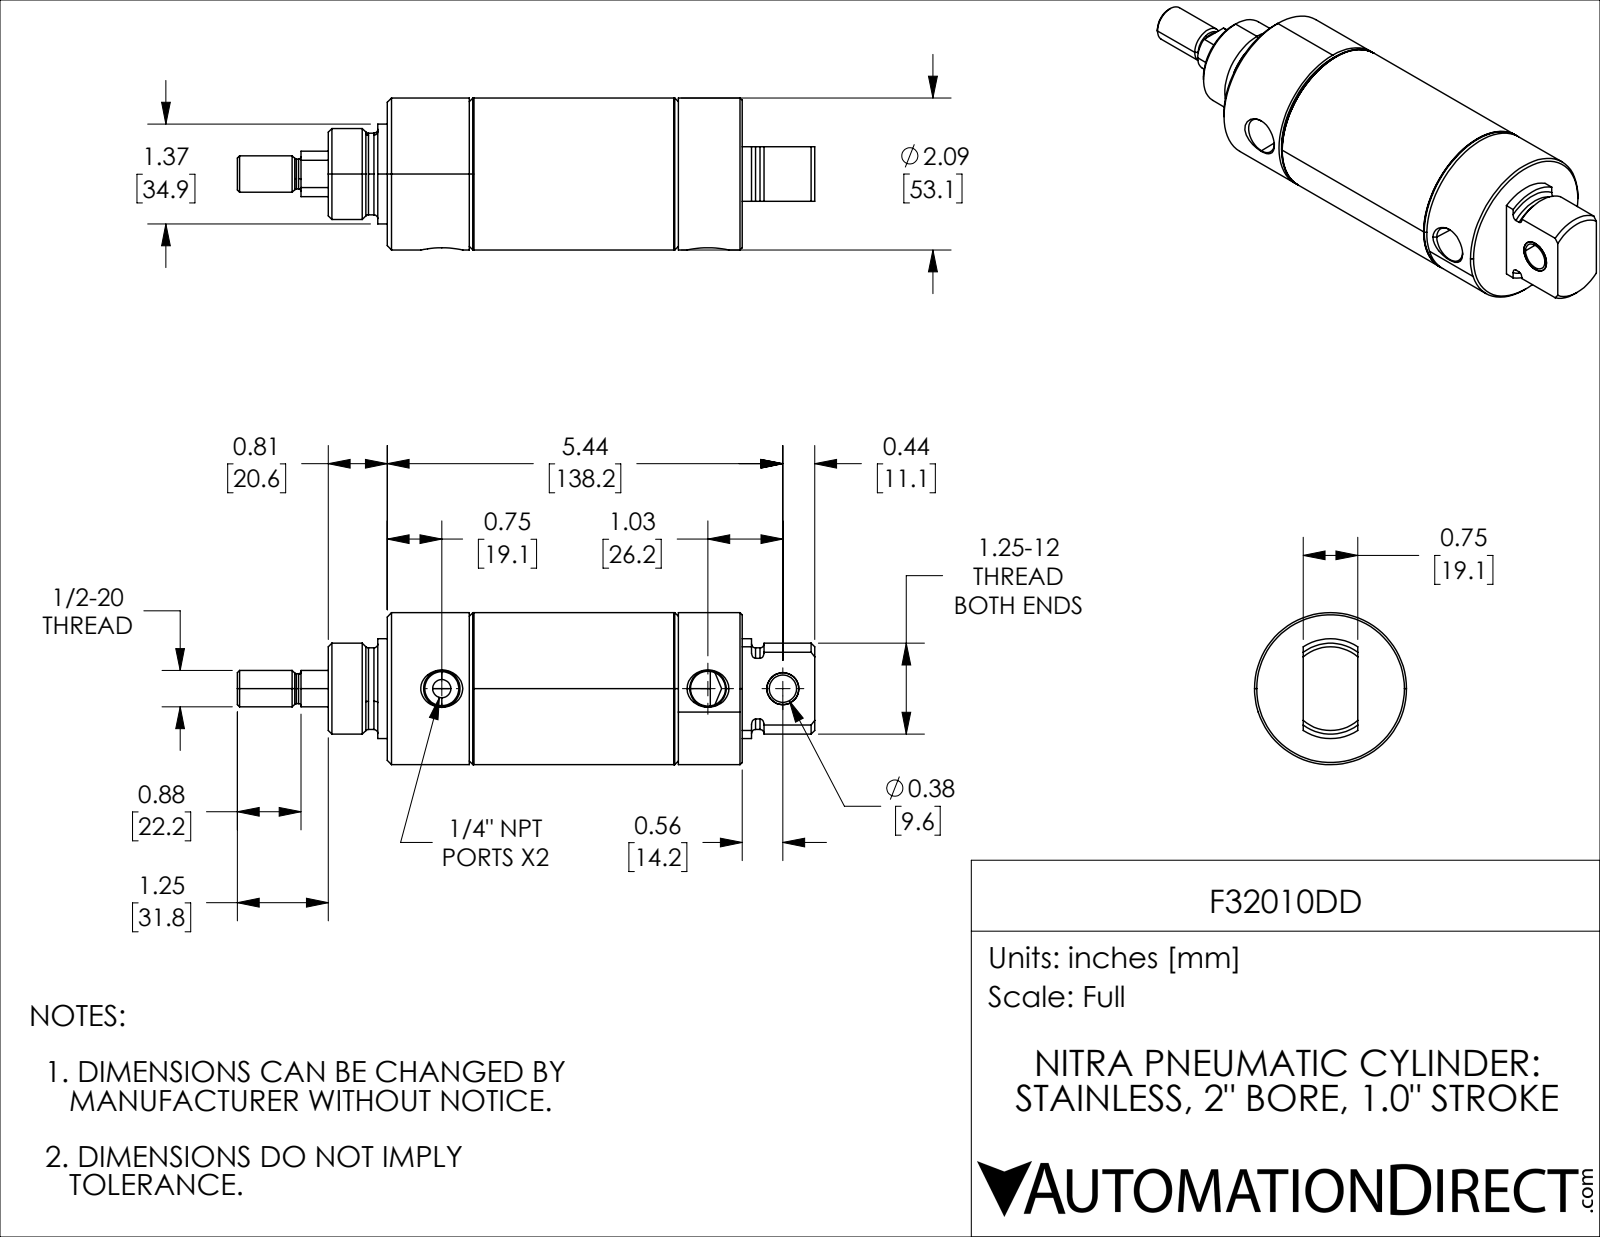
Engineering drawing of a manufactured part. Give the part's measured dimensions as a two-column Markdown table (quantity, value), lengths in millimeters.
| quantity | value |
| --- | --- |
| part name | F32010DD; F32010DD_11; F32010DD_3; F32010DD_5 (+2 more) |
| STEP written by | SolidWorks 2021 (CONFIG_CONTROL_DESIGN) |
| units | millimeters |
| bodies | 5 solids, 160 faces (31 planar, 60 cylindrical, 69 other) |
| overall size | 201.62 × 53.09 × 53.09 |
| volume | 244 803 mm³ |
| surface area | 71 637 mm² |
| round holes (diameter × count) | 6.35 × 1, 9.55 × 1, 11.15 × 1, 12.18 × 1, 16.52 × 1, 19.05 × 1, 49.05 × 1 |
| round bosses / shafts (diameter × count) | 53.09 × 1, 51.16 × 1, 34.87 × 1, 31.75 × 1, 28.51 × 1, 15.88 × 1, 12.7 × 1, 10.46 × 1 |
| partial cylindrical surfaces (radius × count) | 14.25 × 1 |
| main face-to-face distances | 55.58, 30.18, 25.4, 55.57, 85.8, 60.4, 30.22, 30.17, 30.23, 38.15 |
| hole center spacings | 26.17, 92.96, 119.13 |
